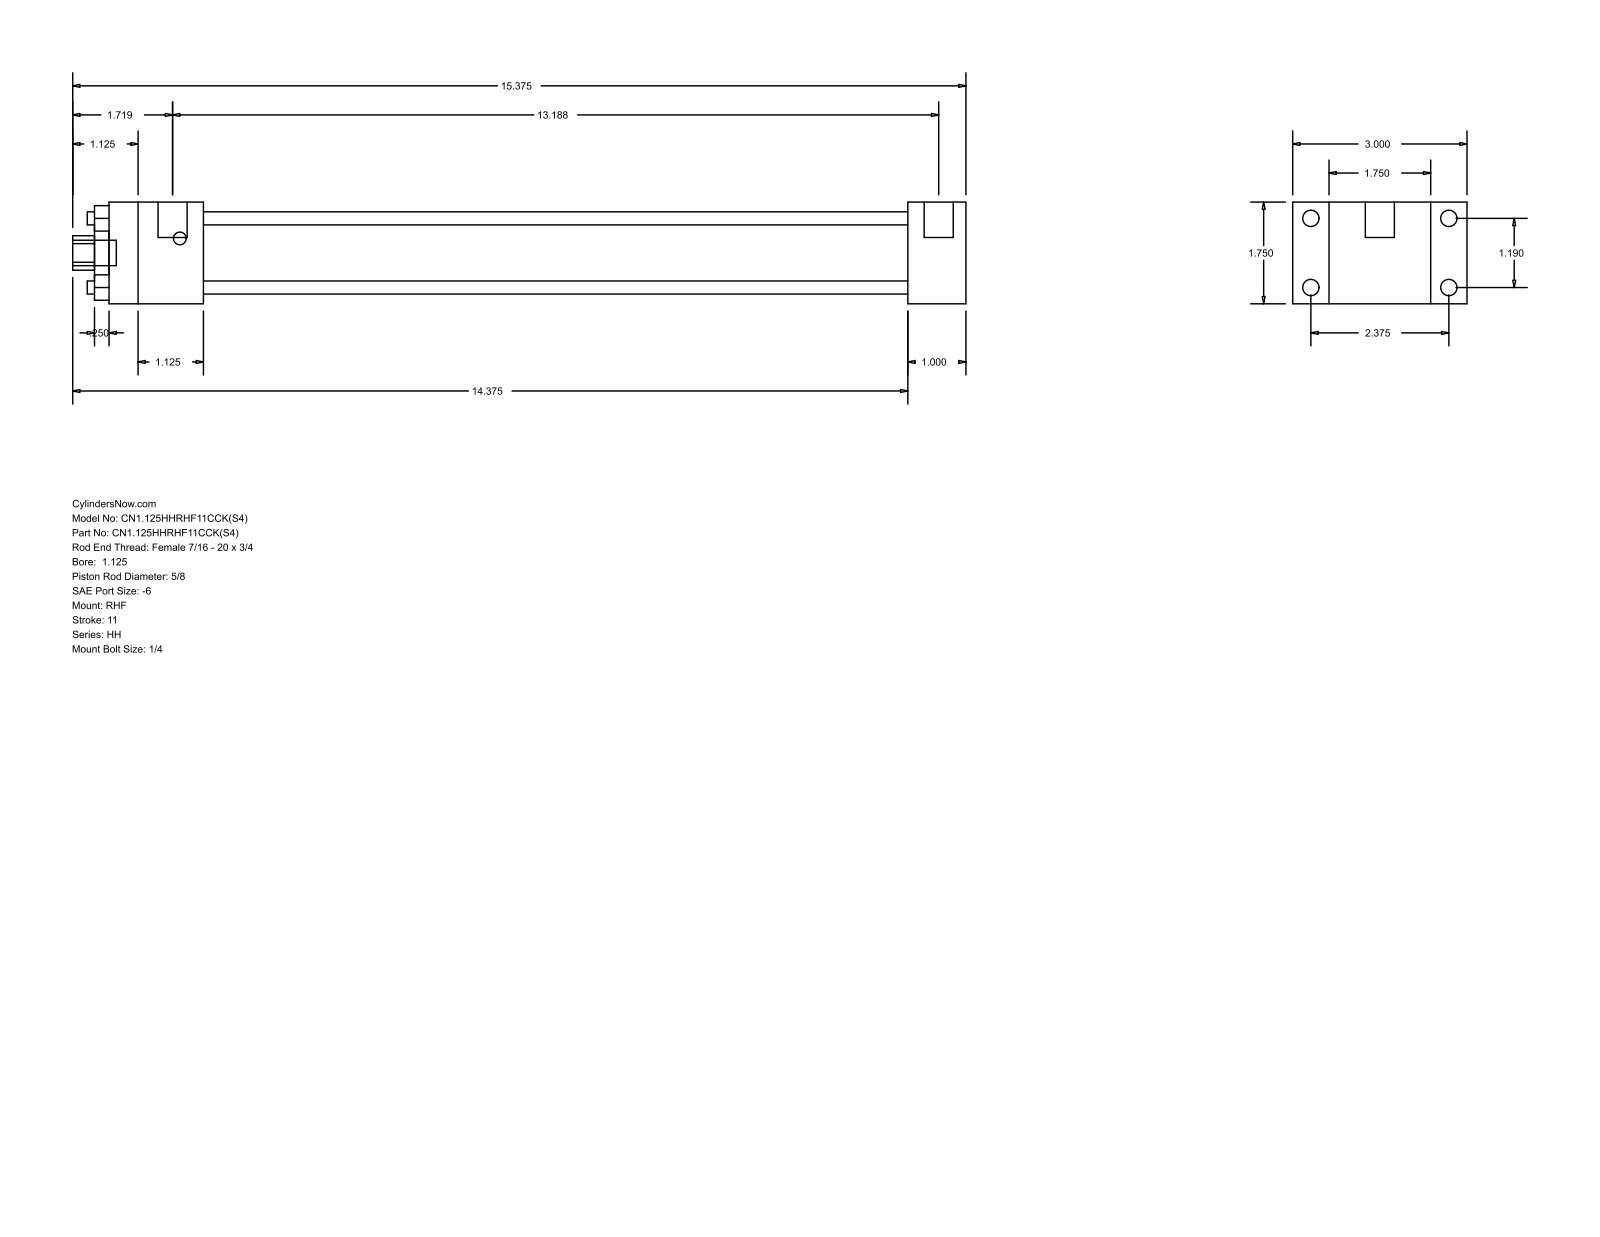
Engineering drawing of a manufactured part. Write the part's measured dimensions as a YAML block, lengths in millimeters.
part_name: "HH_RHF__0112_0.625"
step_written_by: "GSSL Pune (CONFIG_CONTROL_DESIGN)"
units: millimeters
bodies: {solids: 0, faces: 88, planar: 60, cylindrical: 28, other: 0}
overall_size: [390.52, 76.2, 44.45]
round_holes:
  - {diameter: 5.71, count: 4}
  - {diameter: 15.88, count: 1}
  - {diameter: 28.57, count: 1}
  - {diameter: 34.92, count: 1}
round_bosses_or_shafts:
  - {diameter: 7.14, count: 4}
  - {diameter: 5.56, count: 4}
  - {diameter: 12.7, count: 2}
  - {diameter: 11.11, count: 1}
partial_cylinders:
  - {radius: 7.54, count: 1}
face_to_face_distances: [44.46, 15.87, 60.33, 25.4, 76.2, 307.97, 333.37, 41.27, 349.24, 374.64]
hole_center_spacings: [21.37, 30.22, 42.74]
